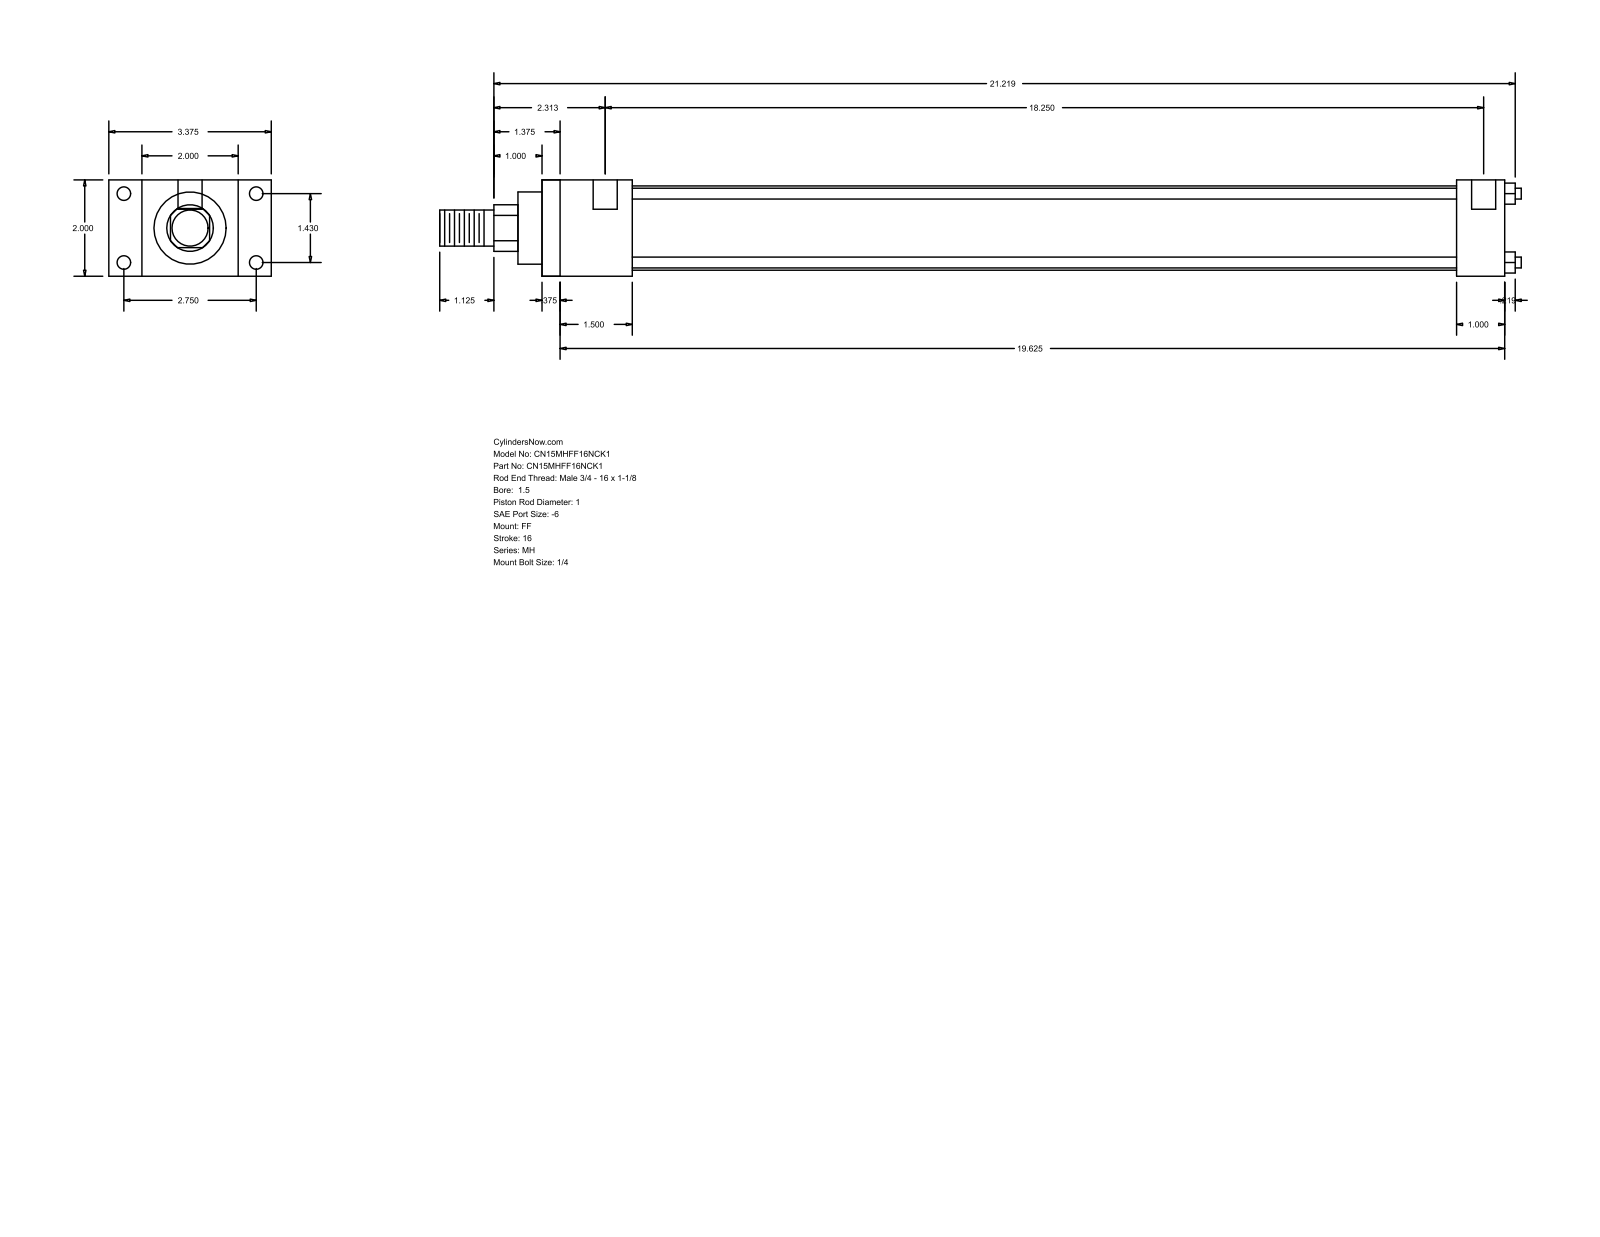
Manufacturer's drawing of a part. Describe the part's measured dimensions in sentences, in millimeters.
The part is named "MH_FF__0150_1". Its 3-D file was written by "GSSL Pune (CONFIG_CONTROL_DESIGN)". It is 0 solids with 92 faces: 64 planar, 28 cylindrical and 0 other. Overall it measures 570.71 by 85.72 by 50.8 millimeters. Round holes: 4 of diameter 5.56, 4 of diameter 7.14, 2 of diameter 12.7. Round bosses or shafts: 4 of diameter 5.71, 1 of diameter 44.45, 1 of diameter 38.1, 1 of diameter 25.4, 1 of diameter 19.05. Partial cylindrical surfaces (rounded edges, fillets, slot ends): 1 of radius 12.29. The main face-to-face distances are 50.8, 508, 9.52, 498.48, 25.4, 17.46, 68.26, 47.63, 38.11, 460.37. The hole center spacings are 36.32, 69.84, 78.72, 466.73, 3.18, 463.55.
